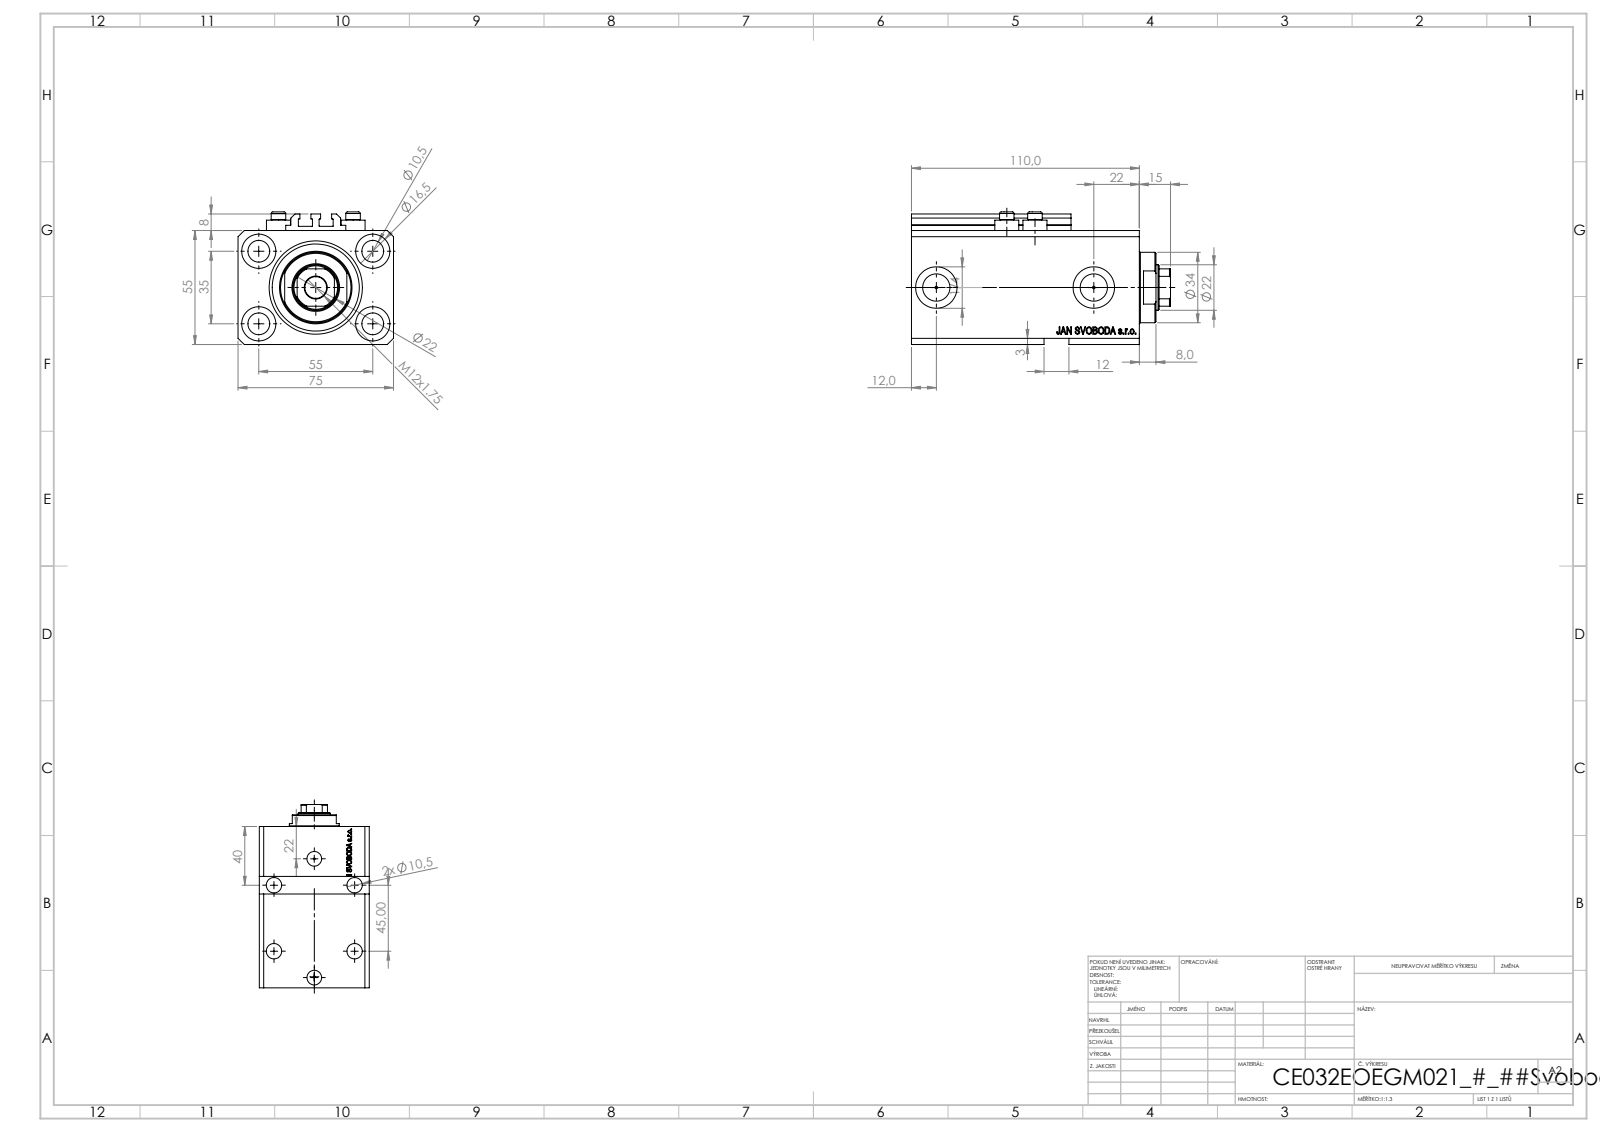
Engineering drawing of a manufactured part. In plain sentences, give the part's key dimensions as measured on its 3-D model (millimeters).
The part is named "V250CE_C_VCP; V250CE_VC_E; V250CE_E_Body; ALLEN BOLT V250CE". Its 3-D file was written by "SolidWorks 2019 (CONFIG_CONTROL_DESIGN)". It is 8 solids with 1084 faces: 514 planar, 146 cylindrical and 424 other. Overall it measures 125 by 75 by 64 millimeters. Its volume is 381 338 cubic millimeters and its surface area 95 642 square millimeters. Round holes: 9 of diameter 10.5, 4 of diameter 1.25, 4 of diameter 4, 4 of diameter 16.5, 2 of diameter 10, 2 of diameter 13.16, 2 of diameter 20, 1 of diameter 22, 1 of diameter 32, 1 of diameter 45. Round bosses or shafts: 4 of diameter 11.6, 4 of diameter 7, 1 of diameter 34. Partial cylindrical surfaces (rounded edges, fillets, slot ends): 10 of radius 0.2, 1 of radius 10.5. The main face-to-face distances are 55, 75, 15, 110, 95, 3, 9.9, 85.1, 100.1, 57. The hole center spacings are 32.6, 32.87, 55, 68.74, 13.6, 14.09, 23.05, 25.81.
